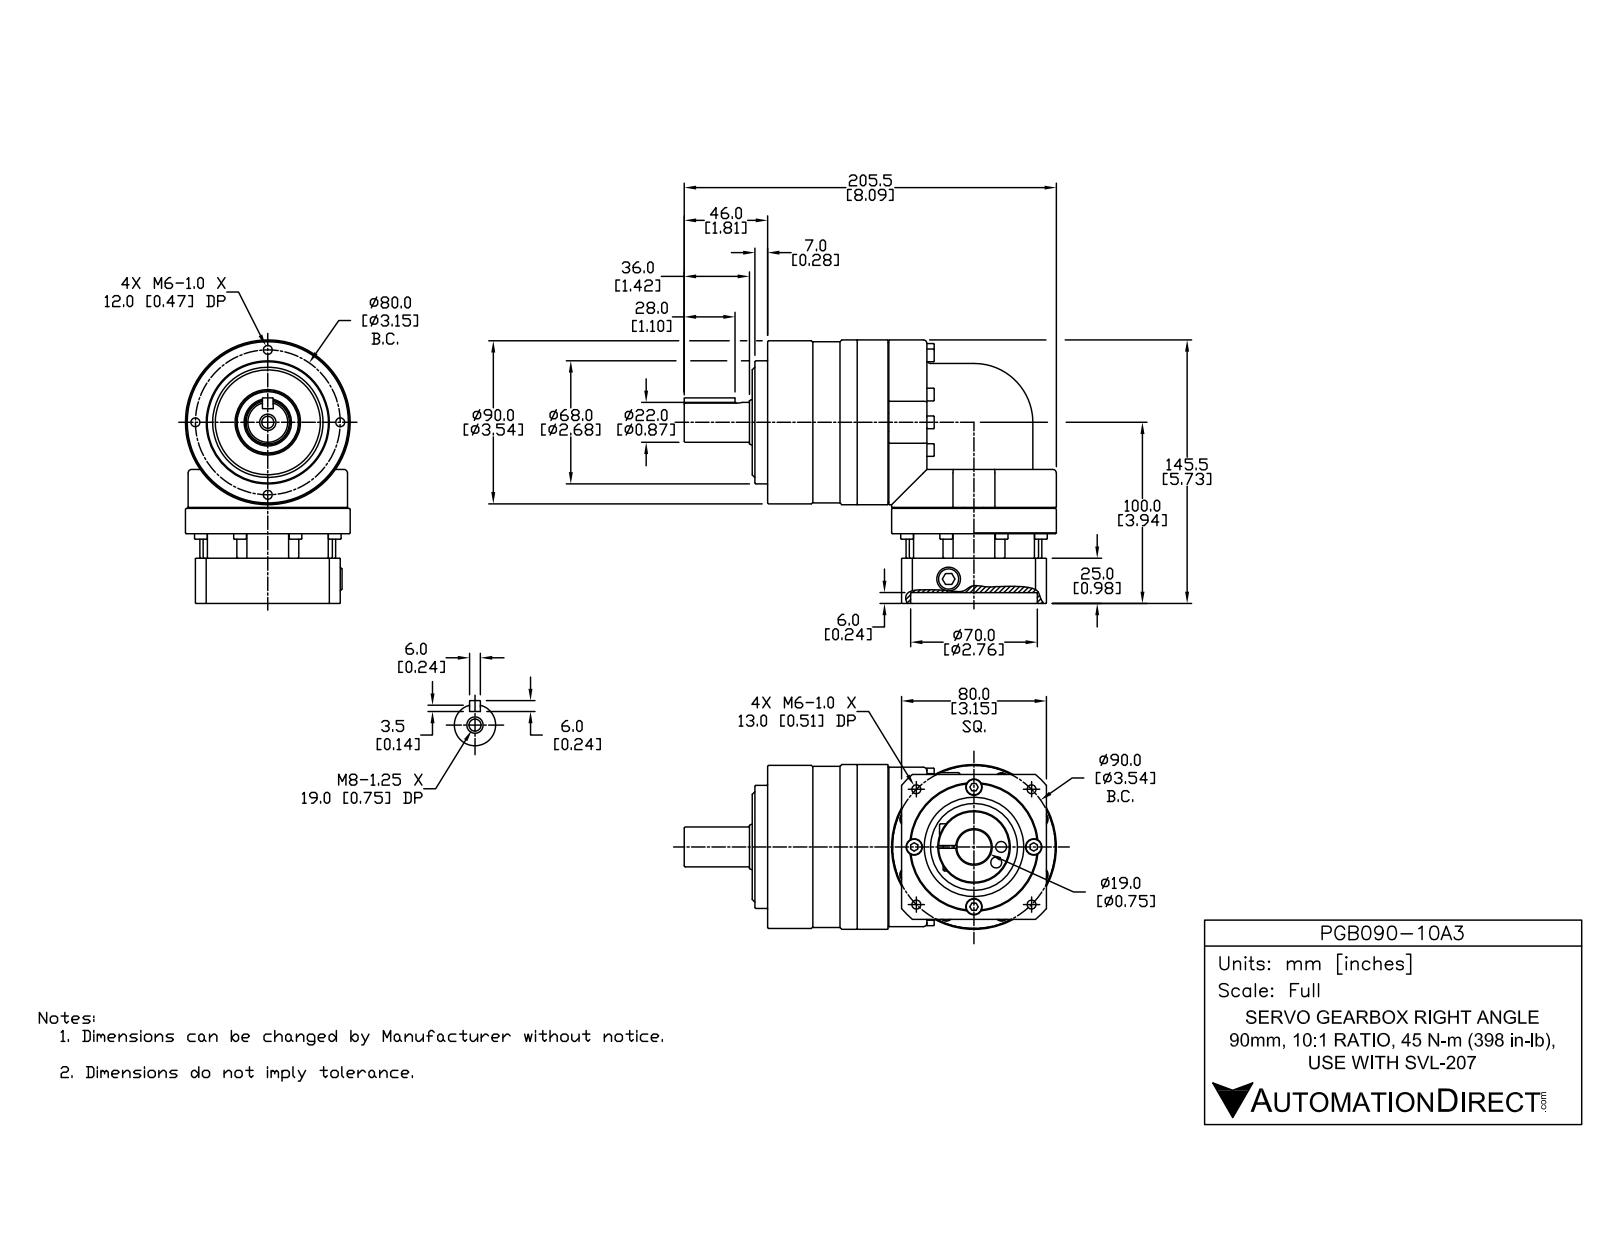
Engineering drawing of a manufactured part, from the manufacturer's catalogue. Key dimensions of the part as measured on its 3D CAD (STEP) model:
Part name (STEP PRODUCT): PGB090-10A3
STEP written by: SolidWorks 2014 (AUTOMOTIVE_DESIGN)
Units: inches
Bodies: 1 solid, 711 faces (284 planar, 195 cylindrical, 232 other)
Overall size (bounding box): 8.091 × 5.728 × 3.583
Volume: 69.72 in³ · Surface area: 153.2 in²
Round holes (diameter × count): ⌀0.177 ×8, ⌀0.194 ×8, ⌀0.315 ×8, ⌀0.354 ×4, ⌀0.236 ×2, ⌀0.256 ×1, ⌀0.262 ×1, ⌀0.413 ×1, ⌀0.748 ×1, ⌀1.89 ×1, ⌀2.165 ×1, ⌀2.756 ×1
Round bosses / shafts (diameter × count): ⌀0.276 ×17, ⌀0.157 ×8, ⌀0.335 ×4, ⌀3.583 ×2, ⌀3.465 ×2, ⌀3.543 ×1, ⌀3.504 ×1, ⌀2.953 ×1
Partial cylindrical surfaces — rounded edges, fillets, slot ends (radius × count): R0.079 ×6, R1.28 ×2, R0.097 ×1, R0.118 ×1, R0.217 ×1, R2.067 ×1
Main face-to-face distances: 2.913, 3.15, 0.984, 0.157, 0.551, 0.335, 0.236, 3.465, 1.398, 0.748
Hole centre spacings: 0.622, 0.681, 1.206, 1.254, 1.575, 1.613, 1.867, 2.228
